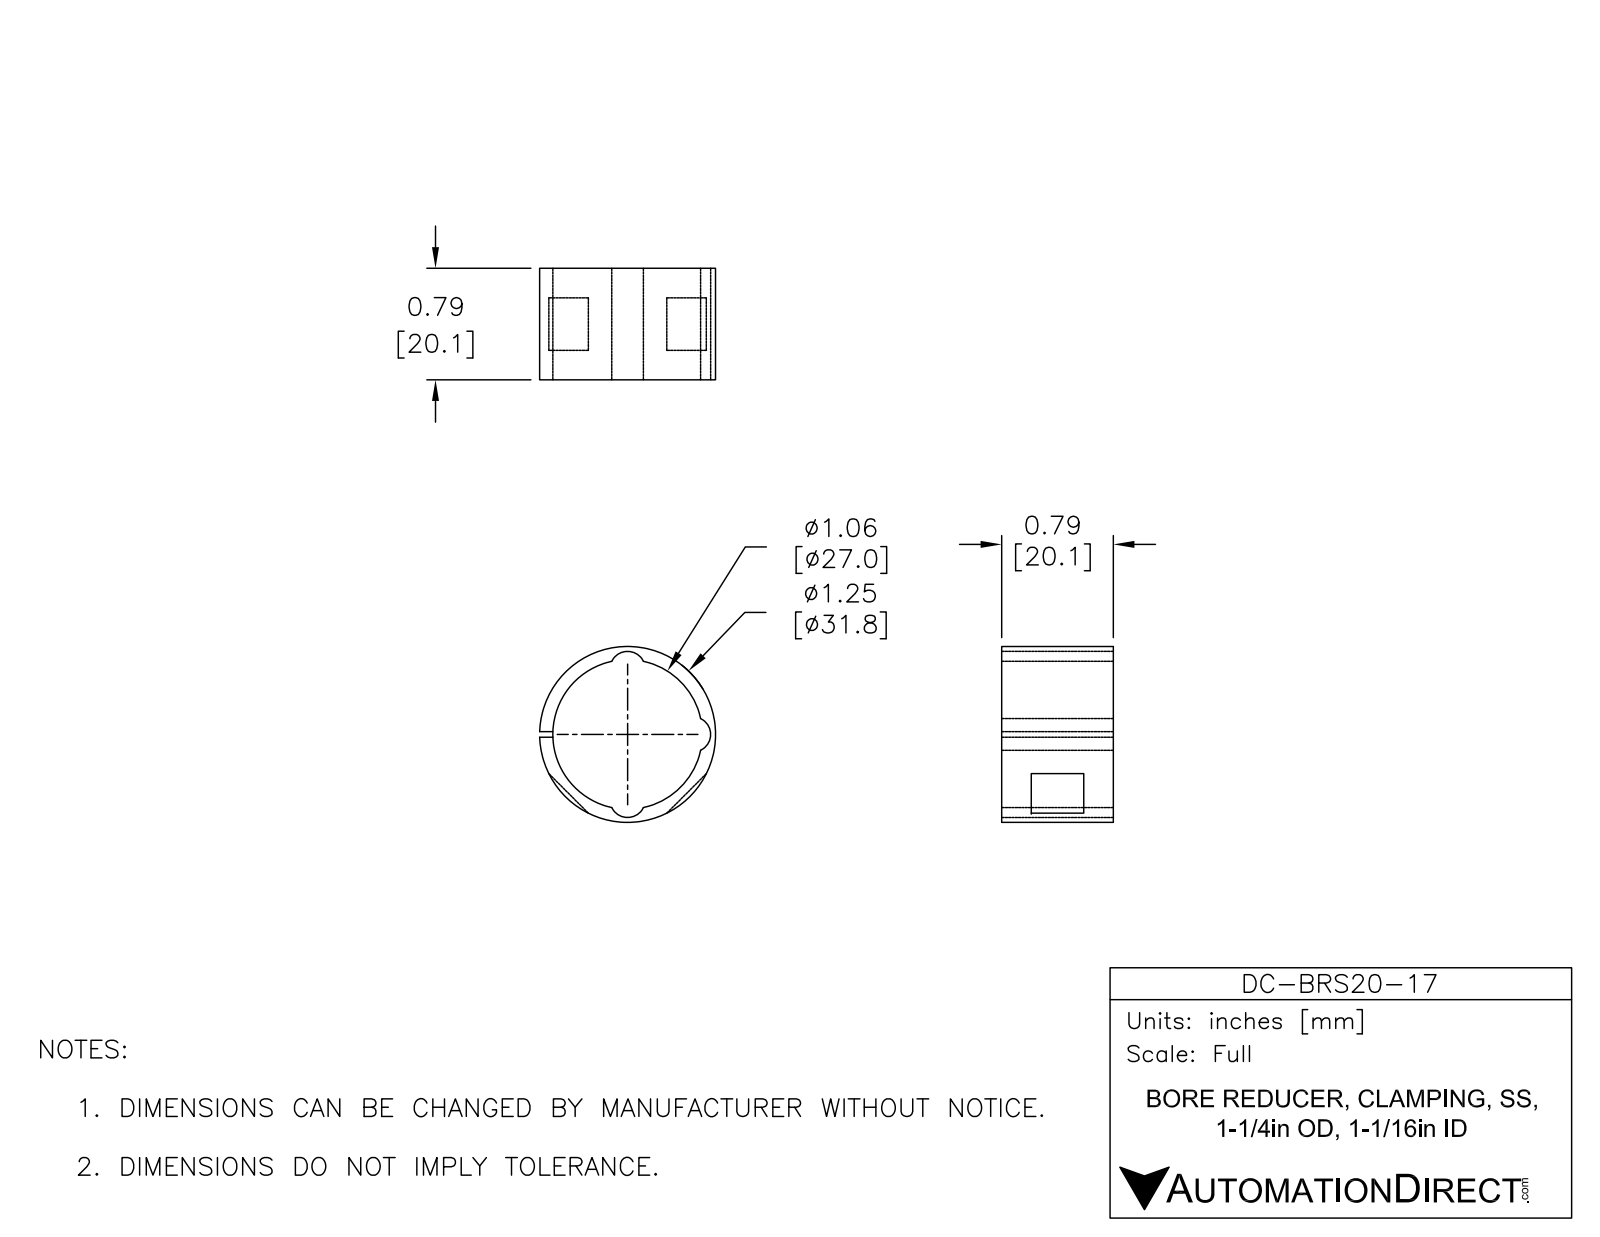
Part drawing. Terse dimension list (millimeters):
name: DC-BR520-17
written by: SolidWorks 2015 (AUTOMOTIVE_DESIGN)
unit: mm
bodies: 1 solid, 21 faces (10 planar, 11 cylindrical, 0 other)
size: 31.75 × 31.74 × 20.14
volume: 3 896 mm³; area: 4 270 mm²
bosses: 1× ⌀31.75
rounds: 3× R3.17, 1× R13.49
face distances: 20.14, 1.02, 5.33, 14.81, 9.48
